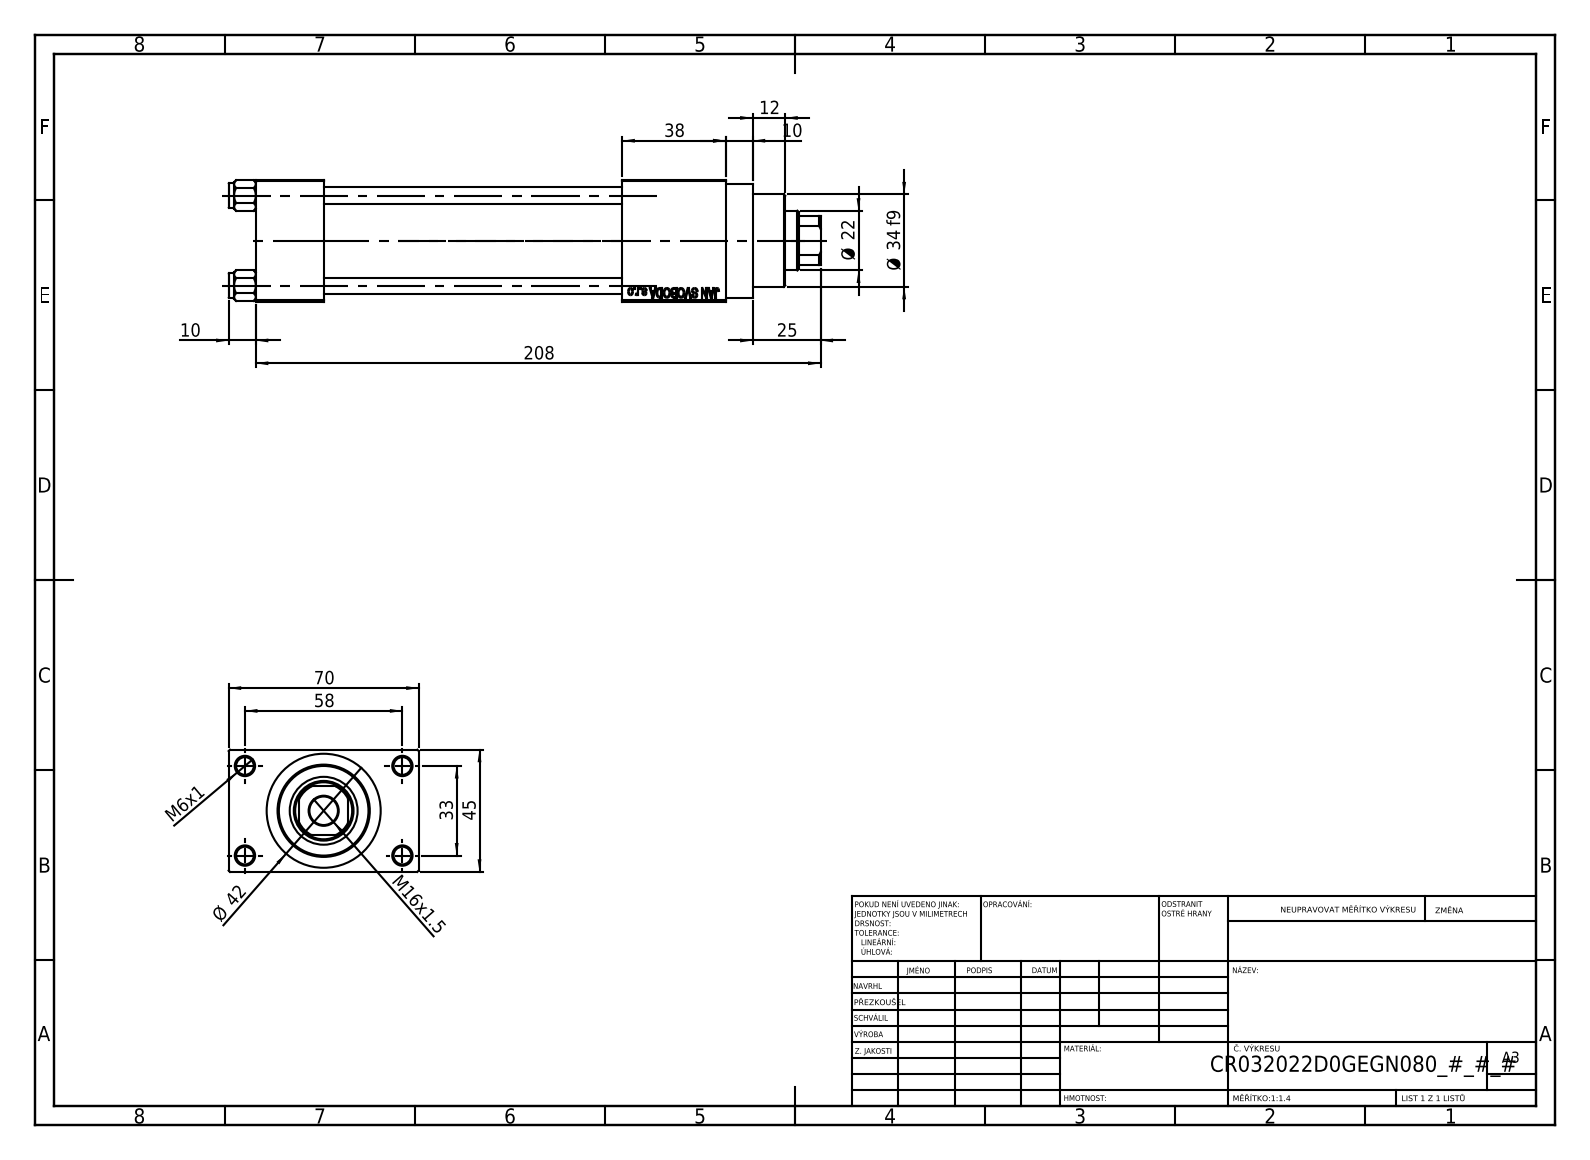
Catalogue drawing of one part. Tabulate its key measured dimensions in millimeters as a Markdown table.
| quantity | value |
| --- | --- |
| part name | V215CR_D_TYCINKA; V215CR_D_Body; V215_VC_A; V215CR_VCP_D (+1 more) |
| STEP written by | SolidWorks 2019 (CONFIG_CONTROL_DESIGN) |
| units | millimeters |
| bodies | 11 solids, 1103 faces (496 planar, 89 cylindrical, 518 other) |
| overall size | 218 × 70 × 45 |
| volume | 294 012 mm³ |
| surface area | 101 320 mm² |
| round holes (diameter × count) | 6 × 4, 6.5 × 4, 7 × 2, 13.16 × 2, 20 × 2, 10.5 × 1, 22 × 1, 24 × 1, 25 × 1, 32 × 1, 33 × 1 |
| round bosses / shafts (diameter × count) | 9 × 4, 42 × 1, 38 × 1, 34 × 1 |
| partial cylindrical surfaces (radius × count) | 10.5 × 1 |
| main face-to-face distances | 45, 25, 12.5, 57.5, 110, 135, 148, 70, 38, 173 |
| hole center spacings | 12.4, 23.48, 33.2, 33.37, 35.35, 45.6, 56.35, 33 |
